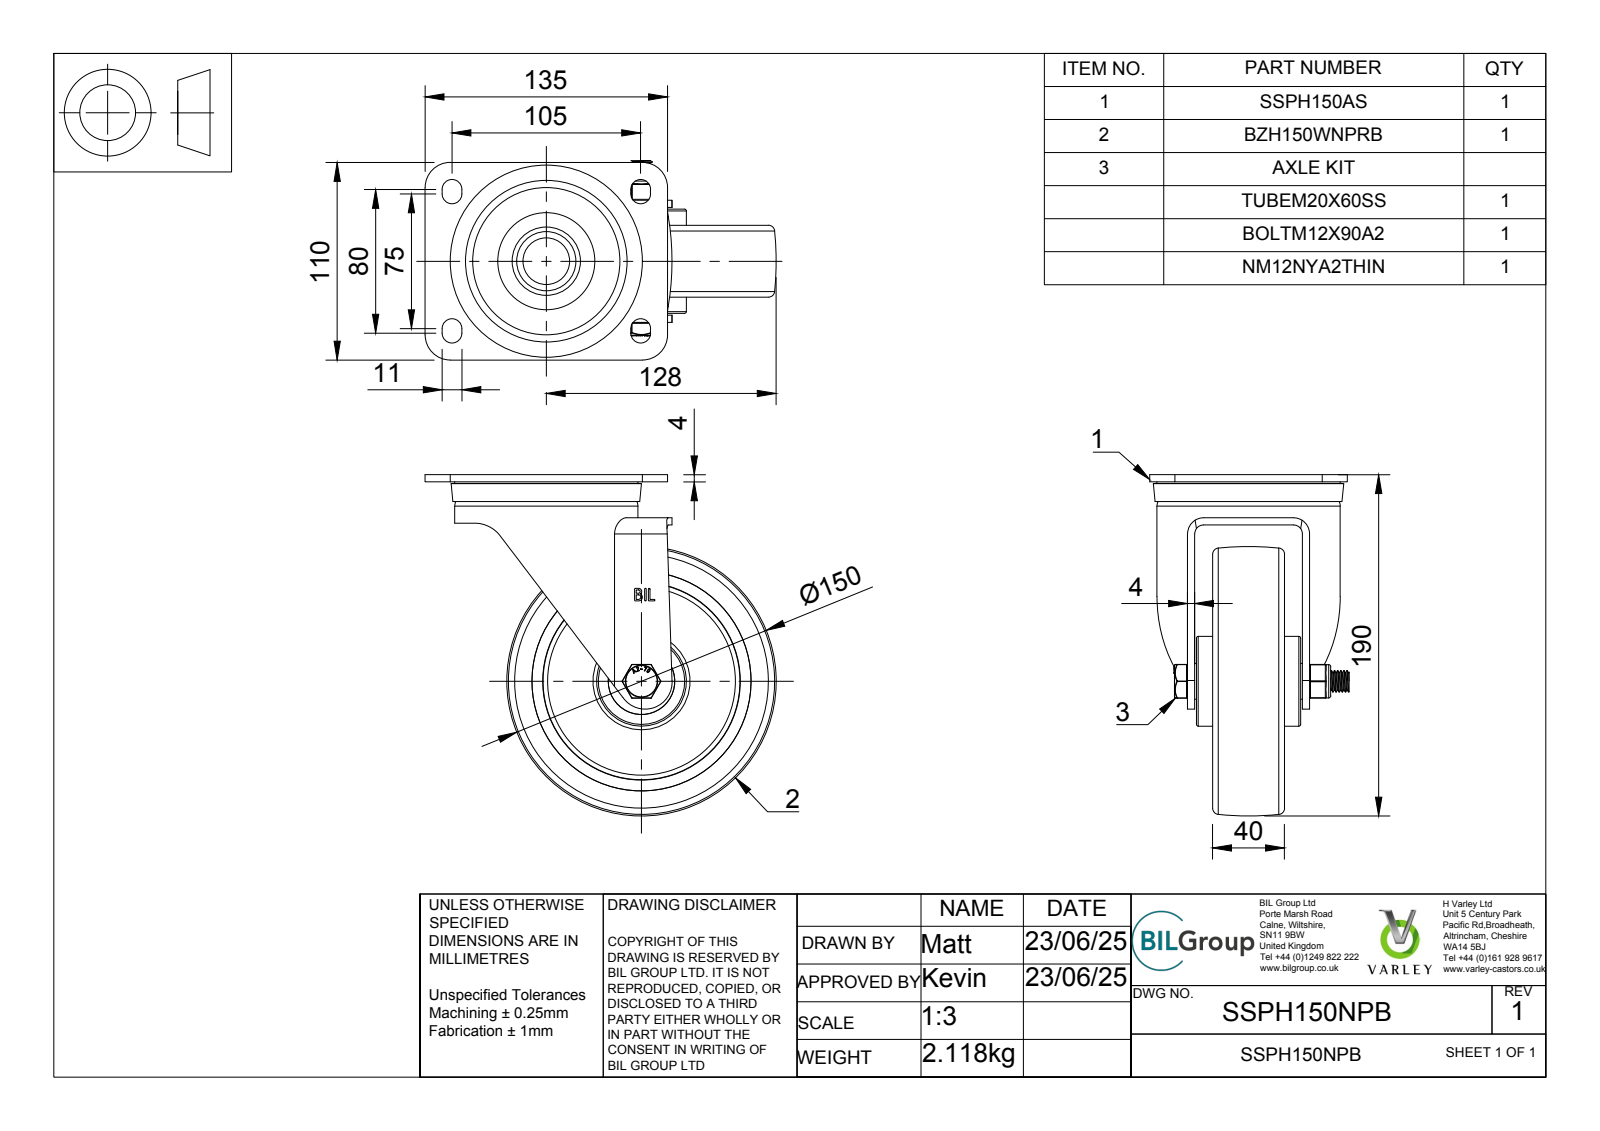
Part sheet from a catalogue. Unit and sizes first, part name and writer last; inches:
Units: inches
Overall size (bounding box): 7.697 × 7.48 × 4.37
Round holes (diameter × count): ⌀0.472 ×1, ⌀0.48 ×1, ⌀0.492 ×1, ⌀0.551 ×1, ⌀0.787 ×1, ⌀0.807 ×1, ⌀1.378 ×1, ⌀1.457 ×1, ⌀3.701 ×1, ⌀4.803 ×1
Round bosses / shafts (diameter × count): ⌀0.295 ×8, ⌀1.339 ×2, ⌀4.016 ×1, ⌀2.913 ×1, ⌀1.969 ×1, ⌀1.299 ×1, ⌀1.024 ×1, ⌀0.906 ×1
Partial cylindrical surfaces — rounded edges, fillets, slot ends (radius × count): R0.02 ×18, R0.01 ×12, R0.217 ×8, R0.551 ×4, R0.197 ×2, R0.354 ×2, R0.531 ×1, R0.591 ×1
Main face-to-face distances: 0.157, 0.669, 0.906, 0.453, 0.236, 0.394, 0.177, 0.295, 0.039, 0.551
Volume: 42 in³ · Surface area: 381.5 in²
Bodies: 19 solids, 573 faces (275 planar, 164 cylindrical, 134 other)
Part name (STEP PRODUCT): SSPH150NPB v3; SSPH150AS v1; STAINLESS STEEL TOP PLATE; STAINLESS STEEL FORKS (+8 more)
STEP written by: Autodesk Translation Framework v14.10.0.0 (AUTOMOTIVE_DESIGN)
